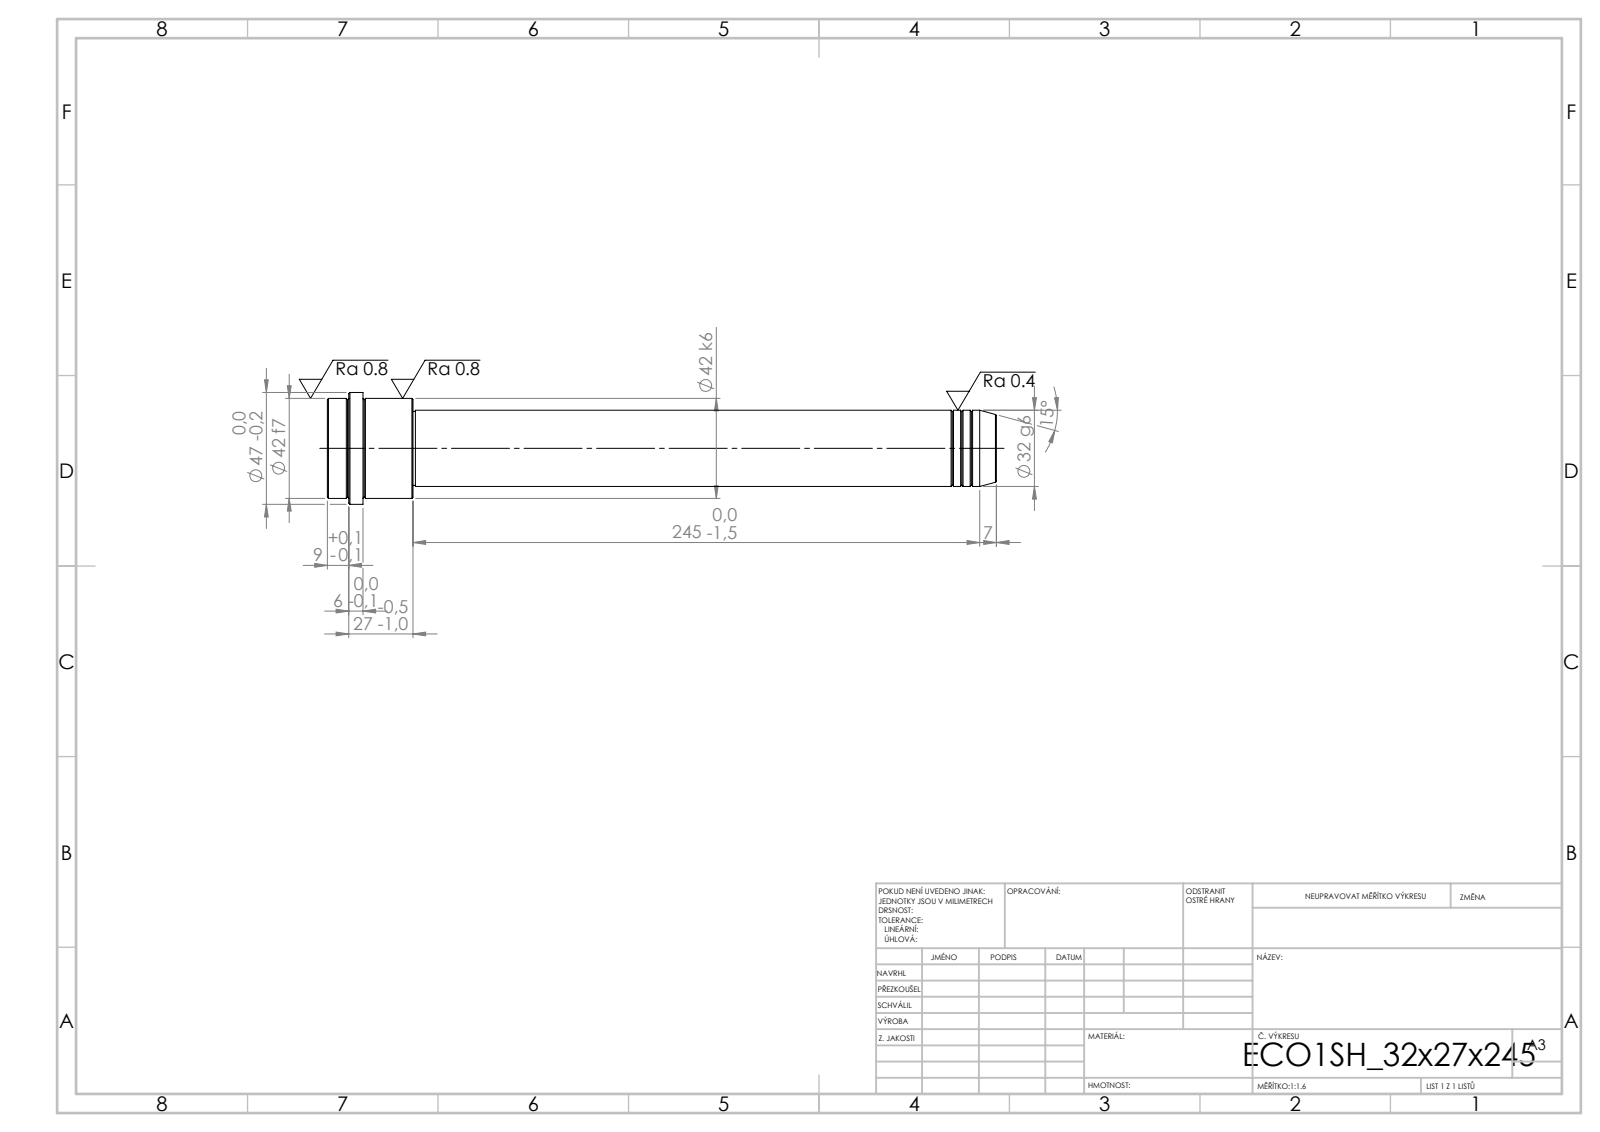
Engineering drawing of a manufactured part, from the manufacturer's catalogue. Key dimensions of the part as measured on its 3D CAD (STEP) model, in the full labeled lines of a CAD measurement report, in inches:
STEP written by: SolidWorks 2019 (CONFIG_CONTROL_DESIGN)
Units: inches
Bodies: 1 solid, 52 faces (6 planar, 16 cylindrical, 30 other)
Overall size (bounding box): 11.063 × 1.85 × 1.85
Volume: 15.14 in³ · Surface area: 51.18 in²
Round bosses / shafts (diameter × count): ⌀1.85 ×1, ⌀1.654 ×1, ⌀1.26 ×1, ⌀1.22 ×1
Main face-to-face distances: 11.063, 9.646, 1.417, 10.472, 0.827, 0.591, 10.709, 1.063, 0.236, 0.354
